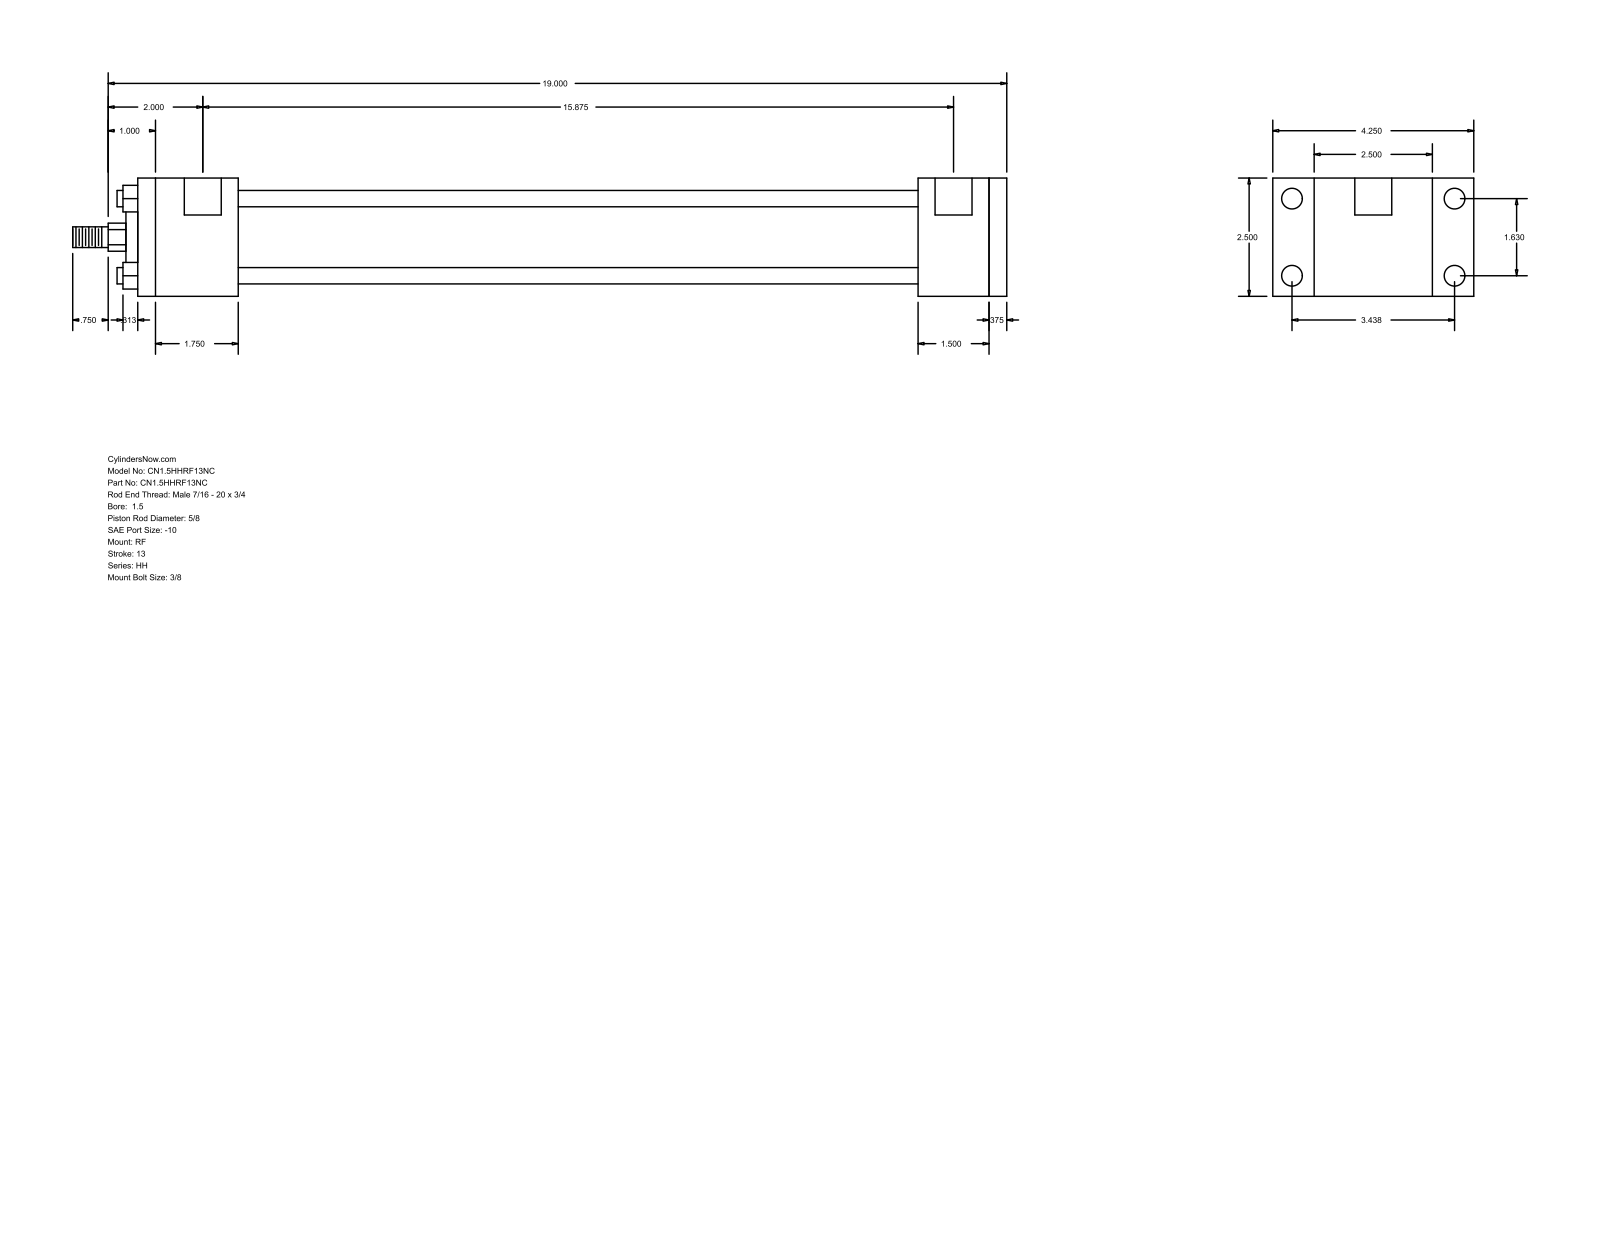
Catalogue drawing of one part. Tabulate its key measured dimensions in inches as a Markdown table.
| quantity | value |
| --- | --- |
| part name | HH_RF__0150_0.625 |
| STEP written by | GSSL Pune (CONFIG_CONTROL_DESIGN) |
| units | inches |
| bodies | 0 solids, 92 faces (64 planar, 28 cylindrical, 0 other) |
| overall size | 19.75 × 4.25 × 2.5 |
| round holes (diameter × count) | 0.219 × 4, 0.438 × 4, 0.781 × 2 |
| round bosses / shafts (diameter × count) | 0.345 × 4, 1.75 × 1, 1.125 × 1, 0.625 × 1, 0.437 × 1 |
| partial cylindrical surfaces (radius × count) | 0.297 × 1 |
| main face-to-face distances | 2.5, 18.375, 0.375, 18, 2.125, 16.5, 14.375, 15.875, 16.25, 1.5 |
| hole center spacings | 0.063, 1.63, 3.438, 3.805, 15.937, 16, 15.875 |
